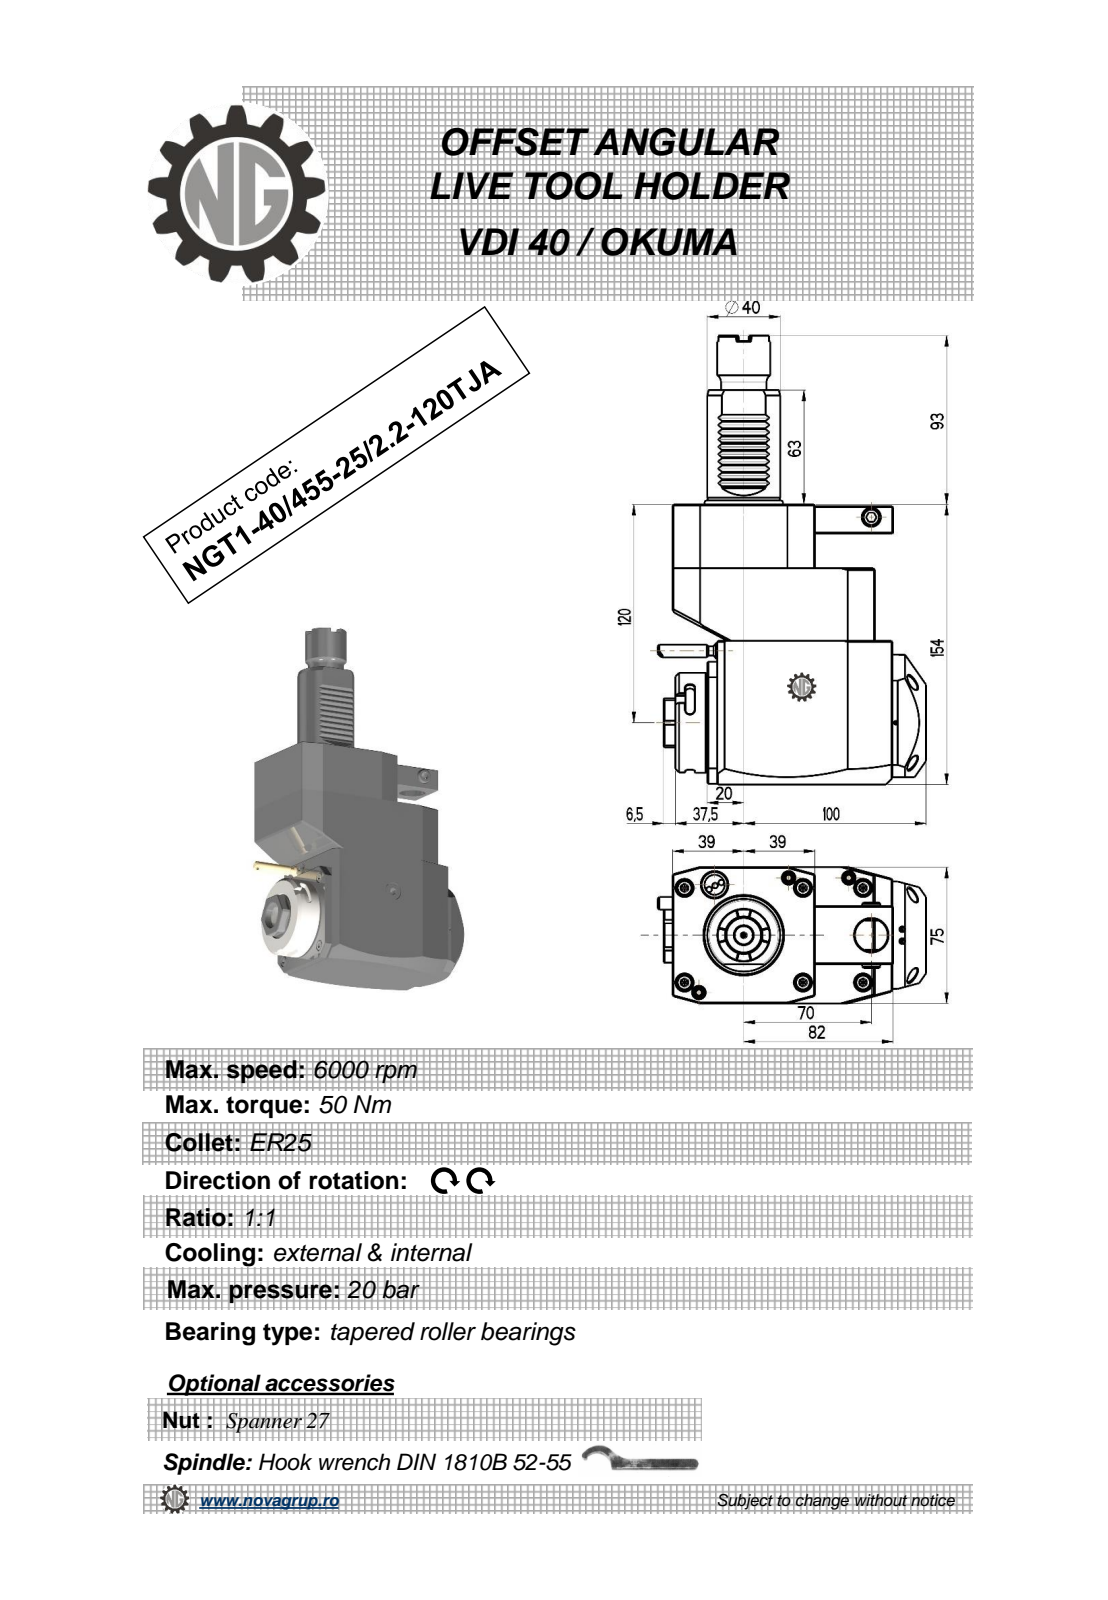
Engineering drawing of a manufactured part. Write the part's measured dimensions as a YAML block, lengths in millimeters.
part_name: "NGT1_40_455_25_1_2_120TJA"
step_written_by: "PRO/ENGINEER BY PARAMETRIC TECHNOLOGY CORPORATION, 2010280 (CONFIG_CONTROL_DESIGN)"
units: millimeters
bodies: {solids: 1, faces: 377, planar: 199, cylindrical: 72, other: 106}
overall_size: [247, 147.33, 75]
volume: 1291000
surface_area: 92587
round_holes:
  - {diameter: 18, count: 2}
  - {diameter: 2.5, count: 1}
  - {diameter: 3, count: 1}
  - {diameter: 9.5, count: 1}
round_bosses_or_shafts:
  - {diameter: 8.96, count: 2}
  - {diameter: 55, count: 1}
  - {diameter: 48, count: 1}
  - {diameter: 40, count: 1}
  - {diameter: 29, count: 1}
  - {diameter: 25, count: 1}
  - {diameter: 10, count: 1}
  - {diameter: 7, count: 1}
partial_cylinders:
  - {radius: 0.3, count: 10}
  - {radius: 2.5, count: 6}
  - {radius: 180, count: 2}
  - {radius: 0.5, count: 1}
  - {radius: 4.25, count: 1}
  - {radius: 10, count: 1}
  - {radius: 15, count: 1}
  - {radius: 24.5, count: 1}
face_to_face_distances: [75, 154, 19, 119, 59, 111, 92, 35, 17.5, 53.5]
hole_center_spacings: [43.2, 75.07, 112.5]
